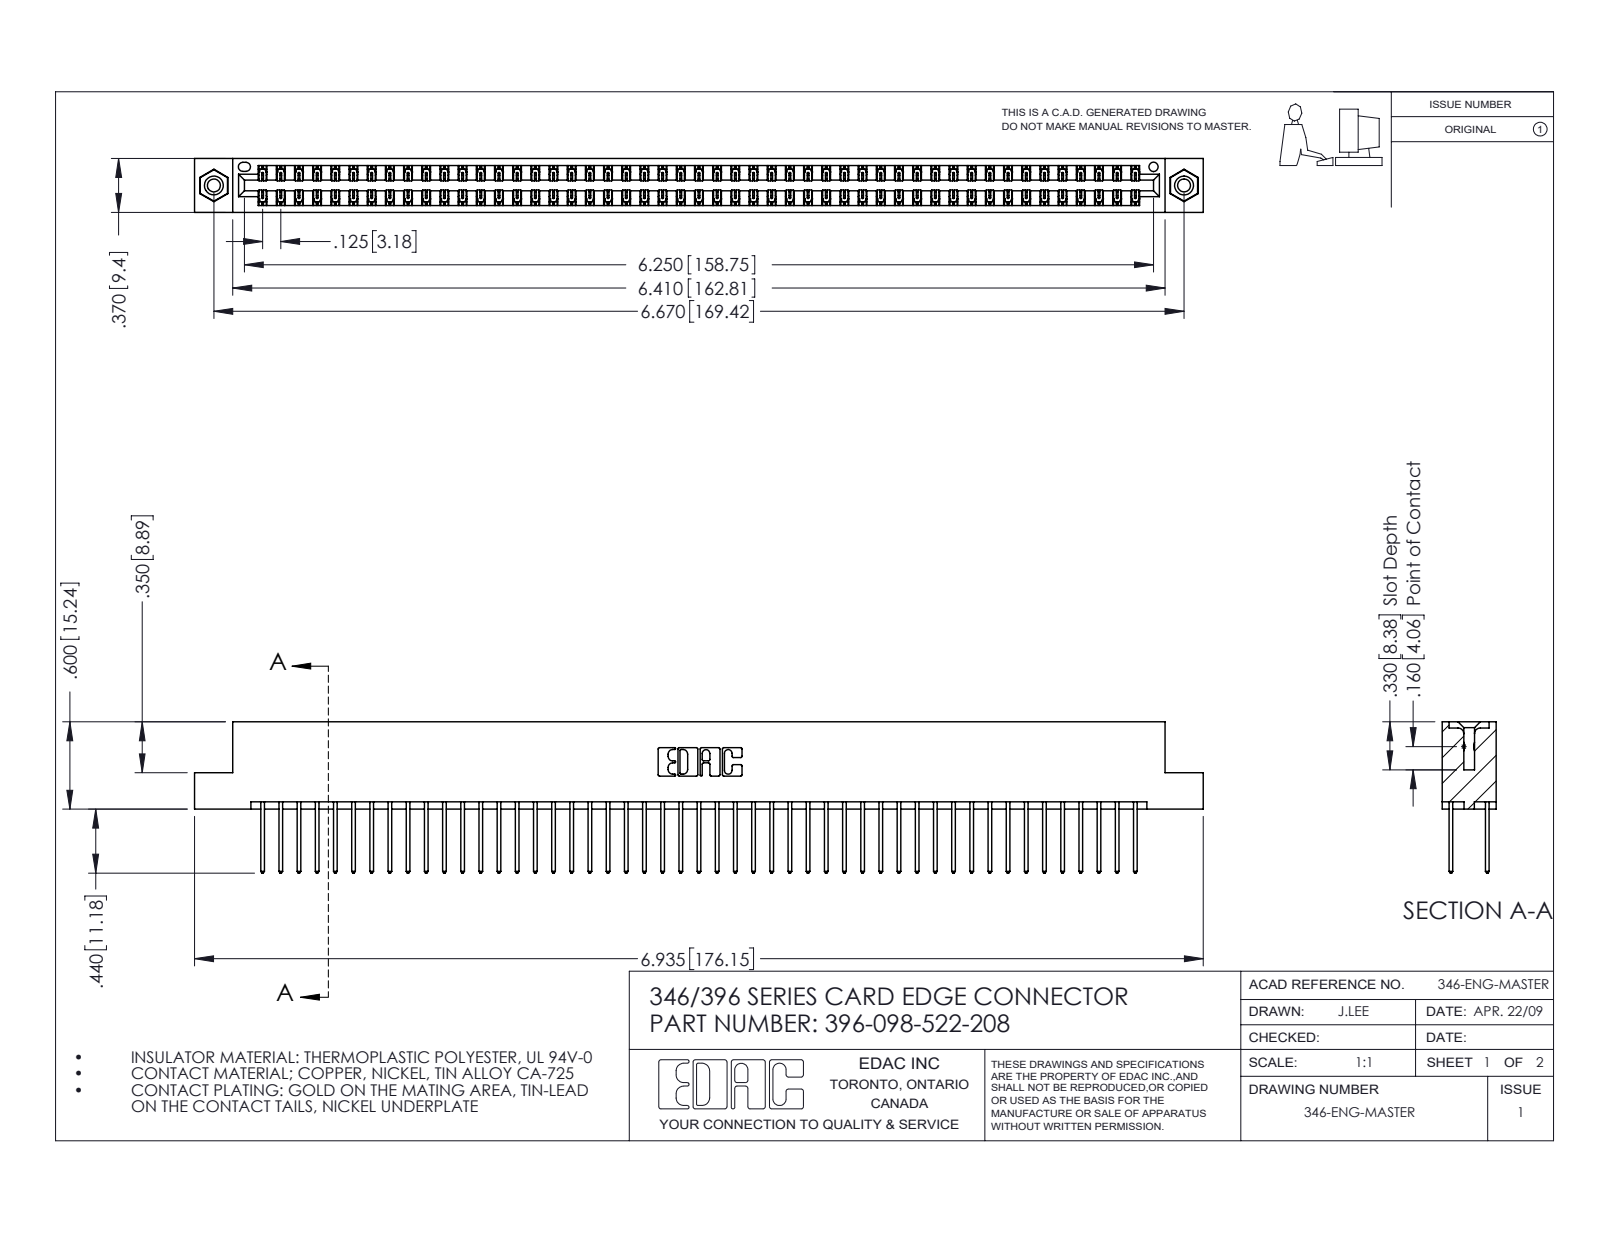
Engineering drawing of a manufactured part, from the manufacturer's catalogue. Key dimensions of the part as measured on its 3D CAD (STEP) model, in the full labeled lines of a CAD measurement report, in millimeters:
Part name (STEP PRODUCT): 345-292-001_345-293-122; 396-098-522-208; 346 Part_Flush Mounting Lugs - 0.156 Dia-TI; 345-250-001_345-250-003-102
STEP written by: SolidWorks 2016 (CONFIG_CONTROL_DESIGN)
Units: millimetres
Bodies: 101 solids, 5278 faces (3538 planar, 1724 cylindrical, 16 other)
Overall size (bounding box): 176.1 × 26.4 × 9.4
Volume: 17 470 mm³ · Surface area: 25 320 mm²
Round holes (diameter × count): ⌀2.3 ×2, ⌀3.2 ×2, ⌀4 ×2, ⌀1.6 ×1
Round bosses / shafts (diameter × count): ⌀3.9 ×2
Partial cylindrical surfaces — rounded edges, fillets, slot ends (radius × count): R0.2 ×147, R0.3 ×98, R0.3 ×22, R0.2 ×6, R0.8 ×6, R0.7 ×3, R0.4 ×2, R0.6 ×2
Main face-to-face distances: 1.2, 8.2, 6.4, 1.8, 7.6, 0.6, 9.4, 7, 3.8, 5.6
Hole centre spacings: 6.2, 164.1, 169.4
